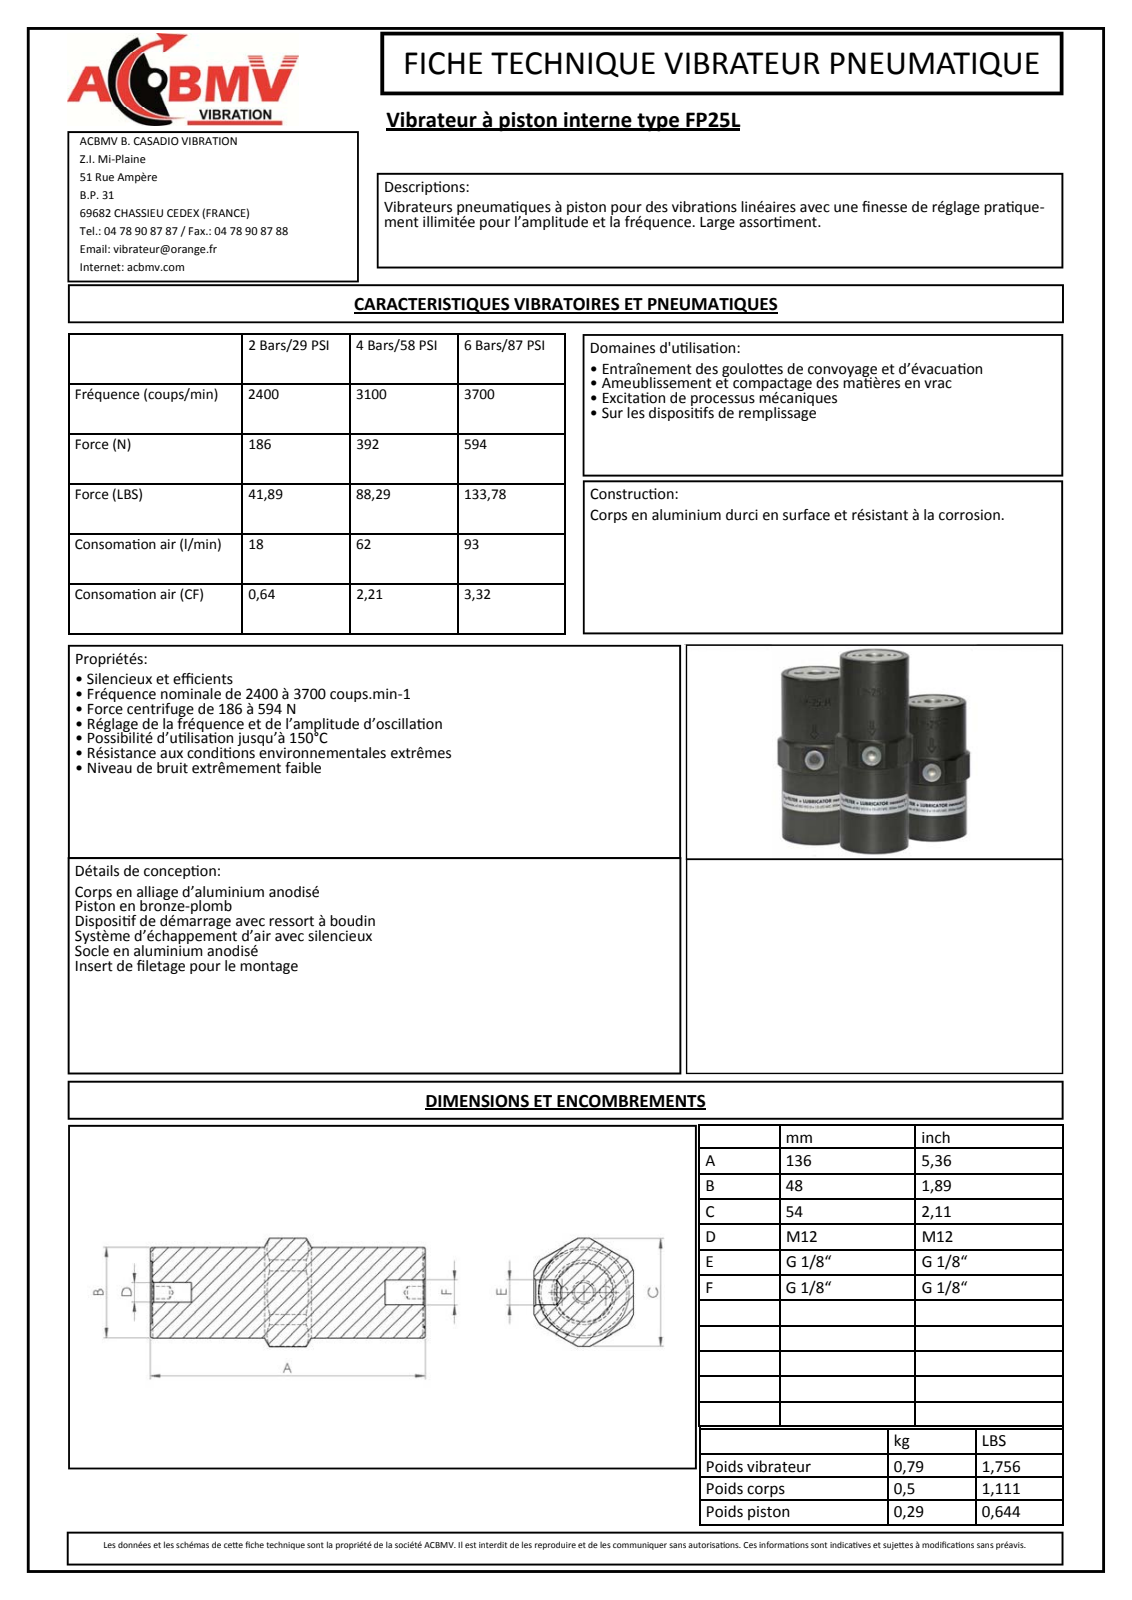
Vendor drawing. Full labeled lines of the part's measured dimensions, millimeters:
Part name (STEP PRODUCT): 9025-30-M
STEP written by: Autodesk Inventor 2011 (CONFIG_CONTROL_DESIGN)
Units: millimetres
Bodies: 1 solid, 442 faces (184 planar, 57 cylindrical, 201 other)
Overall size (bounding box): 136 × 53.5 × 50
Volume: 246 726 mm³ · Surface area: 26 722 mm²
Round holes (diameter × count): ⌀6.2 ×4, ⌀3.2 ×1, ⌀8.57 ×1, ⌀10.11 ×1, ⌀11.45 ×1
Round bosses / shafts (diameter × count): ⌀48 ×1
Partial cylindrical surfaces — rounded edges, fillets, slot ends (radius × count): R14.5 ×1, R23.8 ×1, R24.08 ×1, R24.1 ×1, R26.75 ×1
Main face-to-face distances: 50, 136, 0.5, 135.5, 122.3, 121.8, 13.7, 19, 18.5, 103.3
Hole centre spacings: 1, 11, 12, 23, 22, 24
